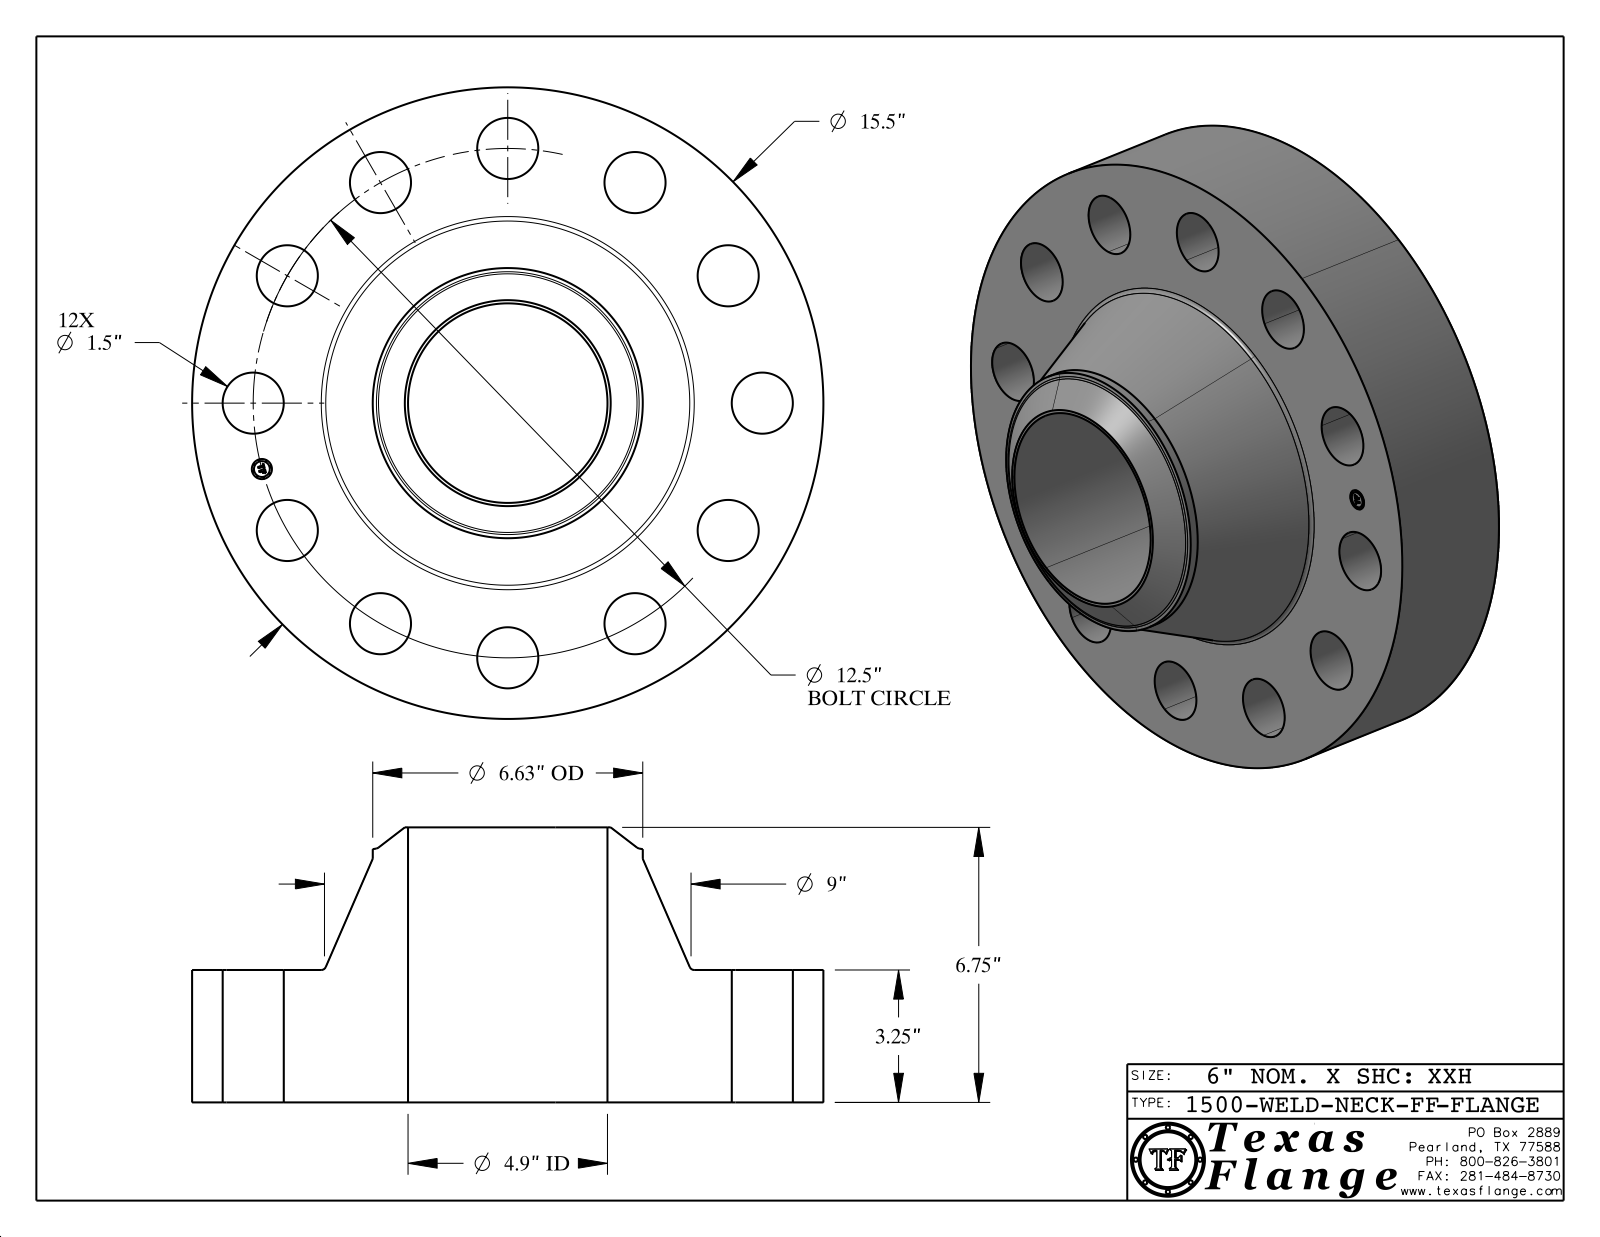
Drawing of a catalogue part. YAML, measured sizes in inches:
part_name: "1500-WELD-NECK-FF"
step_written_by: "CATIA V5 STEP AP214 (AUTOMOTIVE_DESIGN)"
units: inches
bodies: {solids: 1, faces: 428, planar: 368, cylindrical: 50, other: 10}
overall_size: [15.5, 15.5, 6.75]
volume: 571.3
surface_area: 794.8
round_holes:
  - {diameter: 1.5, count: 12}
  - {diameter: 0.495, count: 1}
  - {diameter: 4.897, count: 1}
round_bosses_or_shafts:
  - {diameter: 0.03, count: 8}
  - {diameter: 15.5, count: 1}
  - {diameter: 6.63, count: 1}
  - {diameter: 0.39, count: 1}
face_to_face_distances: [3.25, 6.75, 3.5, 3.235, 0.015, 3.515, 0.148, 0.144, 0.027, 0.096]
hole_center_spacings: [6.25, 8.839, 3.235, 10.826, 12.074, 12.5, 3.235, 6.25]
